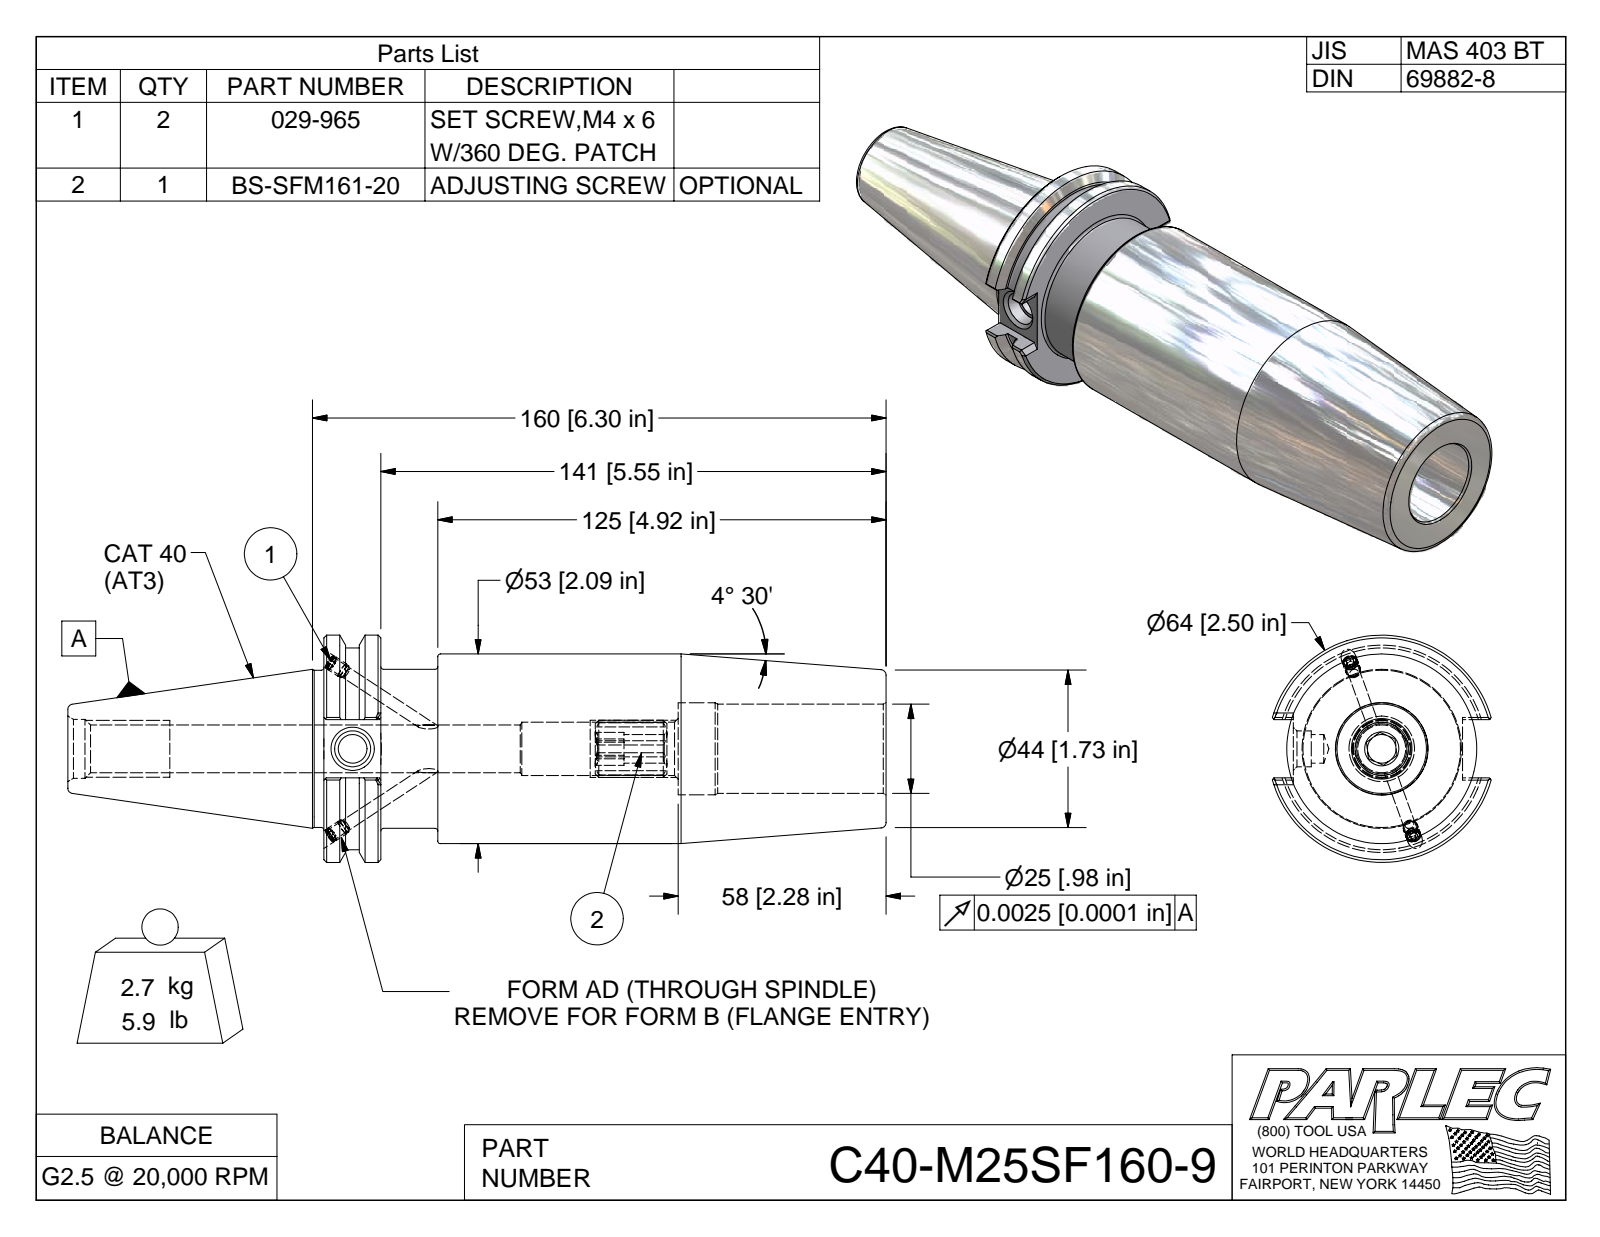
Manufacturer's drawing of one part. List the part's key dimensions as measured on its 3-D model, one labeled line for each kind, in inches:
Part name (STEP PRODUCT): C40-M25SF160-9; C40BC-M25SF160-9-1; 029-965; BS-SFM161-20
STEP written by: Autodesk Inventor 2009 (AUTOMOTIVE_DESIGN)
Units: inches
Bodies: 4 solids, 134 faces (66 planar, 23 cylindrical, 45 other)
Overall size (bounding box): 8.987 × 2.5 × 2.403
Volume: 20.81 in³ · Surface area: 83.3 in²
Round holes (diameter × count): ⌀0.13 ×2, ⌀0.161 ×2, ⌀0.983 ×1, ⌀1.013 ×1
Round bosses / shafts (diameter × count): ⌀0.165 ×2, ⌀0.157 ×2, ⌀2.5 ×1, ⌀2.219 ×1, ⌀2.087 ×1, ⌀1.75 ×1, ⌀1.73 ×1
Partial cylindrical surfaces — rounded edges, fillets, slot ends (radius × count): R0.315 ×1
Main face-to-face distances: 0.625, 6.174, 5.549, 1.25, 4.924, 3.891, 3.266, 2.641, 2.283, 0.64
